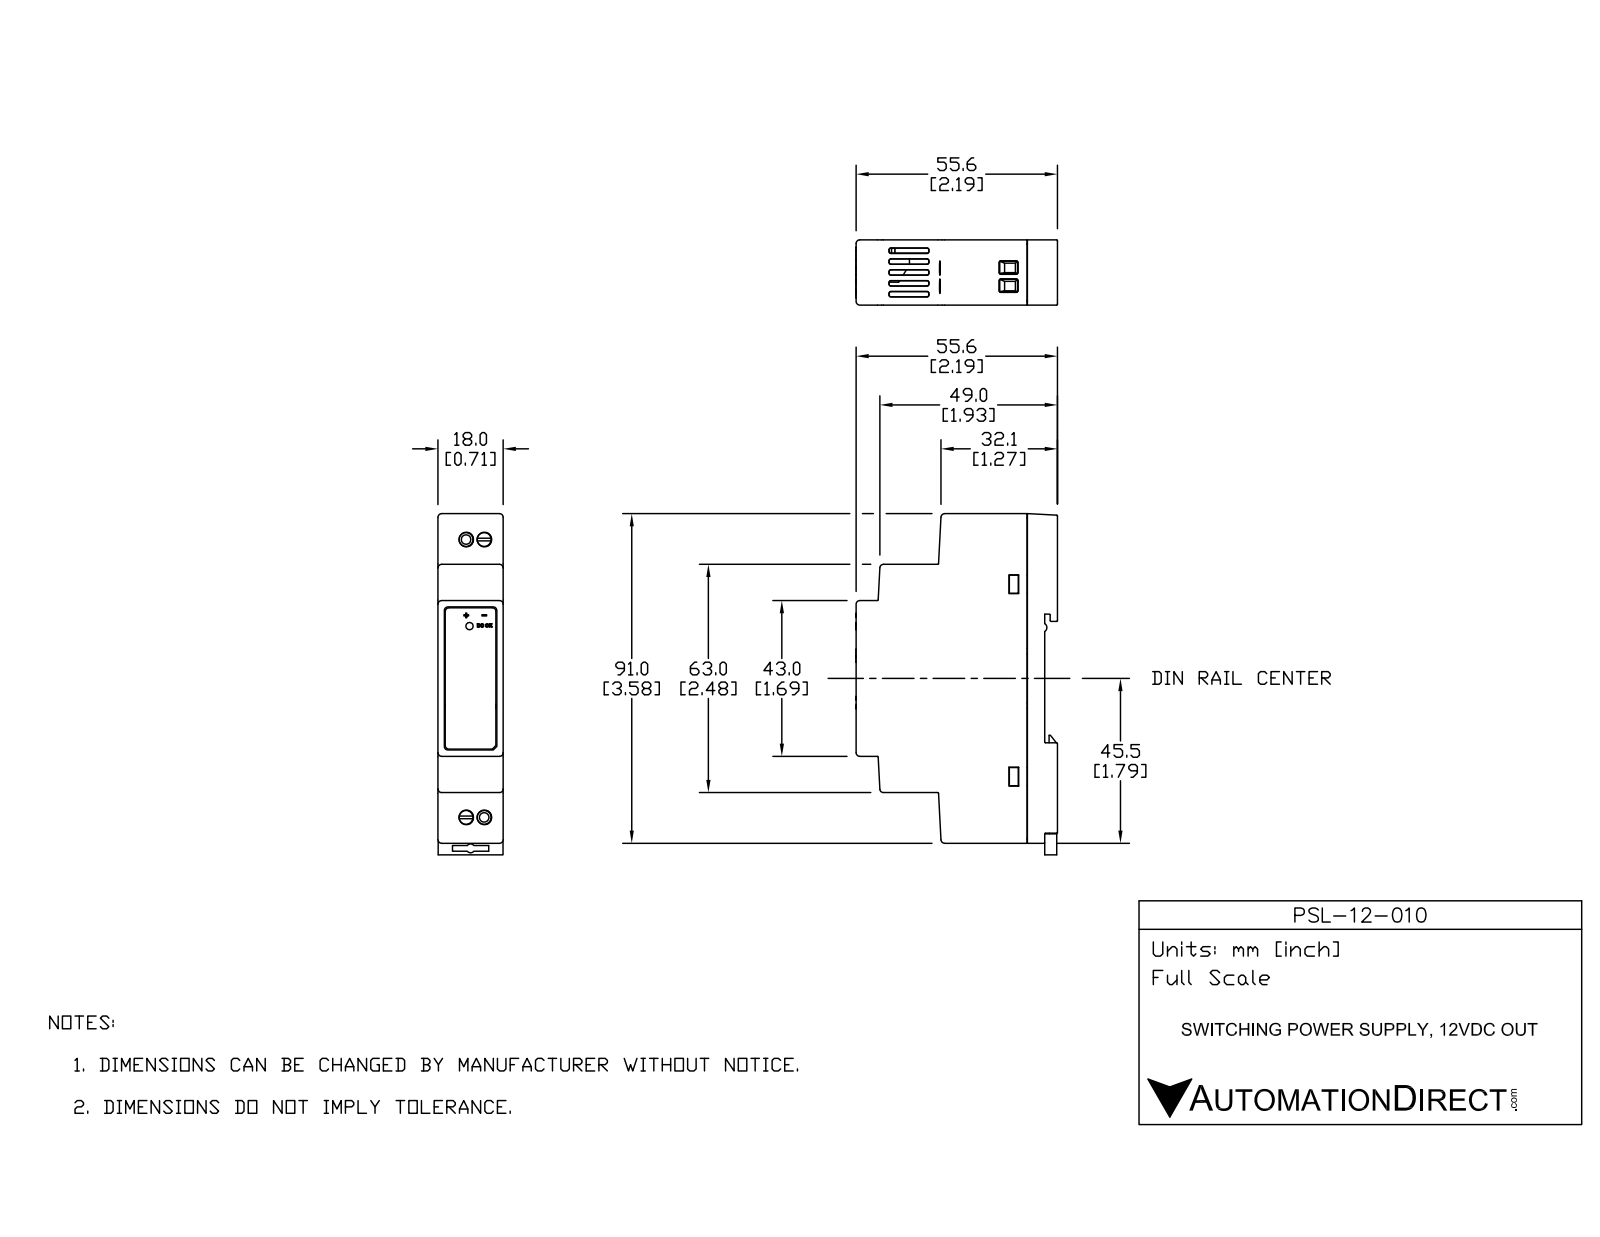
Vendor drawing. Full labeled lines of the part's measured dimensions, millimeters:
Part name (STEP PRODUCT): PSL-12-010
STEP written by: SolidWorks 2017 (AUTOMOTIVE_DESIGN)
Units: millimetres
Bodies: 12 solids, 934 faces (589 planar, 267 cylindrical, 78 other)
Overall size (bounding box): 94.2 × 55.6 × 18
Volume: 26 220 mm³ · Surface area: 39 630 mm²
Round holes (diameter × count): ⌀2.6 ×4, ⌀4 ×4, ⌀4 ×4, ⌀3 ×1, ⌀4.1 ×1
Round bosses / shafts (diameter × count): ⌀3.8 ×2, ⌀0.9 ×2
Partial cylindrical surfaces — rounded edges, fillets, slot ends (radius × count): R0.2 ×87, R0.5 ×58, R1 ×35, R0.1 ×17, R0.8 ×8, R1.5 ×6, R3.1 ×2, R1.2 ×1
Main face-to-face distances: 18, 1, 13.3, 4.7, 14.3, 3.7, 1.3, 5.8, 4.5, 1.6
Hole centre spacings: 76.7, 76.9, 5, 5, 5.1, 23.9, 52.8, 53
